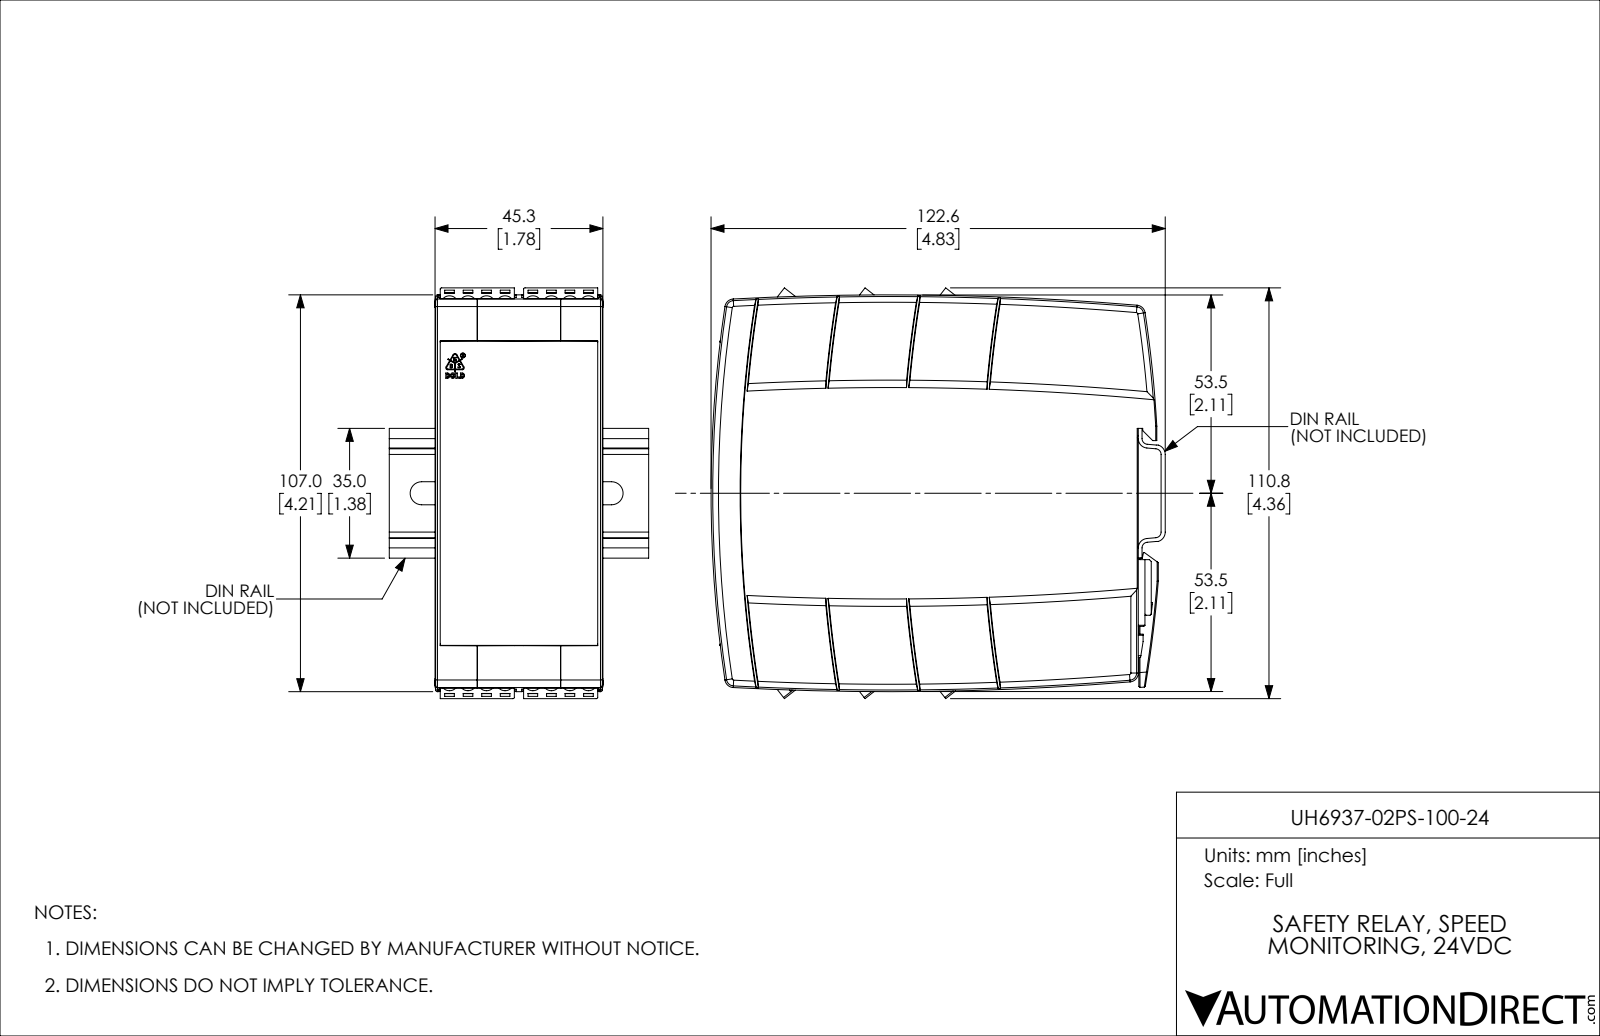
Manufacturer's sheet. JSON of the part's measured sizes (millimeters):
{"part_name": "UH6937-02PS-100-24", "step_written_by": "SolidWorks 2018 (AUTOMOTIVE_DESIGN)", "units": "millimeters", "bodies": {"solids": 17, "faces": 9587, "planar": 7538, "cylindrical": 1783, "other": 266}, "overall_size": [120.7, 110.8, 45.3], "volume_mm3": 108100, "surface_area_mm2": 122800, "round_holes": [[1.5, 48], [3.2, 48], [4, 48], [0.7, 6], [0.8, 6], [1.2, 1]], "round_bosses_or_shafts": [[3.8, 48], [2, 6], [1.3, 1]], "partial_cylinders_radius": [[2.9, 48], [0.4, 37], [0.1, 18], [0.3, 18], [0.3, 18], [0.3, 18], [0.1, 12], [0.2, 12]], "face_to_face_distances": [1.1, 43.7, 42.6, 1.3, 43.9, 45.1, 17.1, 22.5, 44.9, 2], "hole_center_spacings": [5, 10, 22.5, 17.5, 27.5, 26.2, 12.5, 14.3]}
